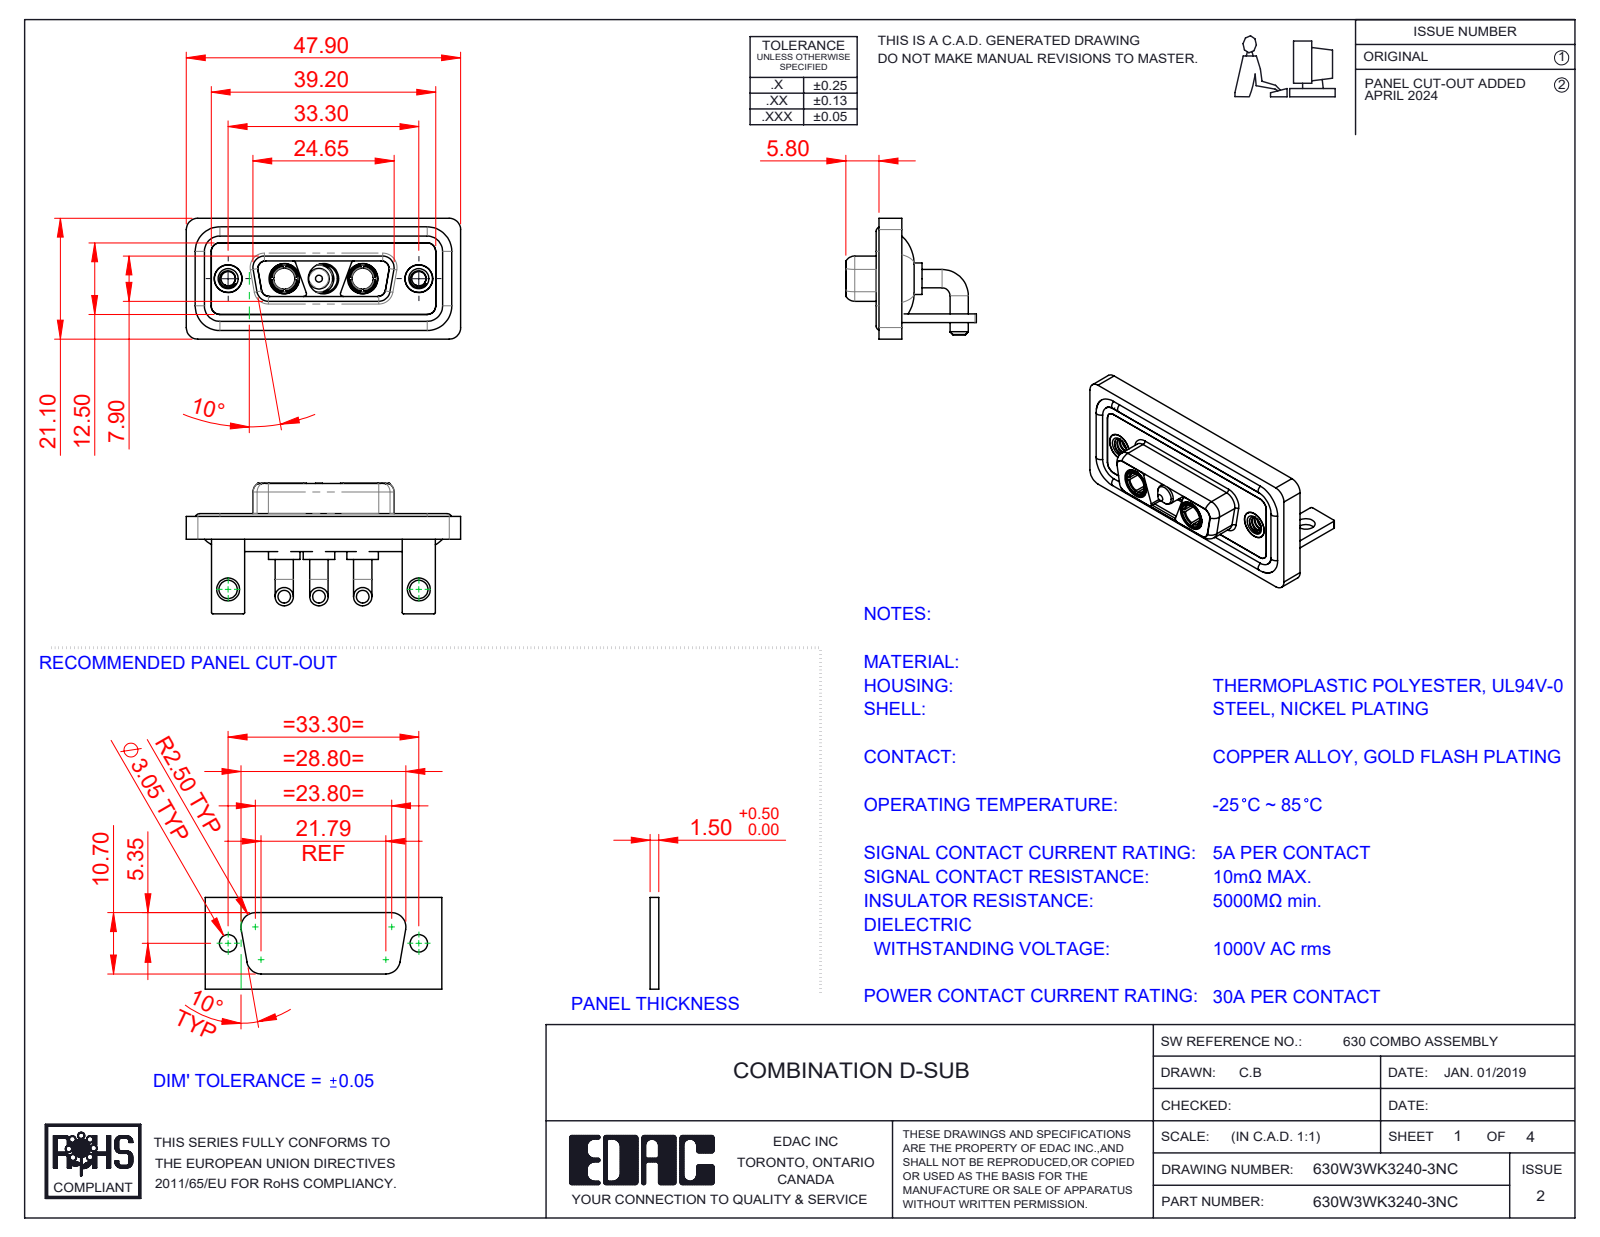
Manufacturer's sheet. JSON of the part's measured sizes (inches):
{"part_name": "630Combo Waterproof Housing_15 Contacts; 630Combo Shell Front_15 Contacts; 630W3WK3240-3NC; 630Combo Stabilizer Bracket_50 Contacts (+5 more)", "step_written_by": "SolidWorks 2023 (CONFIG_CONTROL_DESIGN)", "units": "inches", "bodies": {"solids": 15, "faces": 637, "planar": 198, "cylindrical": 286, "other": 153}, "overall_size": [1.886, 0.898, 0.831], "volume_in3": 0.395, "surface_area_in2": 16.32, "round_holes": [[0.191, 5], [0.209, 3], [0.098, 2], [0.126, 2], [0.146, 2], [0.157, 2], [0.159, 2], [0.197, 2]], "round_bosses_or_shafts": [[0.126, 6], [0.063, 4], [0.217, 3], [0.205, 3], [0.187, 3], [0.148, 3], [0.195, 2], [0.195, 2]], "partial_cylinders_radius": [[0.079, 21], [0.059, 18], [0.01, 16], [0.053, 12], [0.02, 9], [0.063, 8], [0.024, 4], [0.026, 4]], "face_to_face_distances": [0.016, 0.114, 0.059, 0.146, 0.071, 0.043, 0.161, 0.063, 0.098, 0.055], "hole_center_spacings": [0.27, 0.386, 0.656, 0.925, 1.311, 0.539]}
